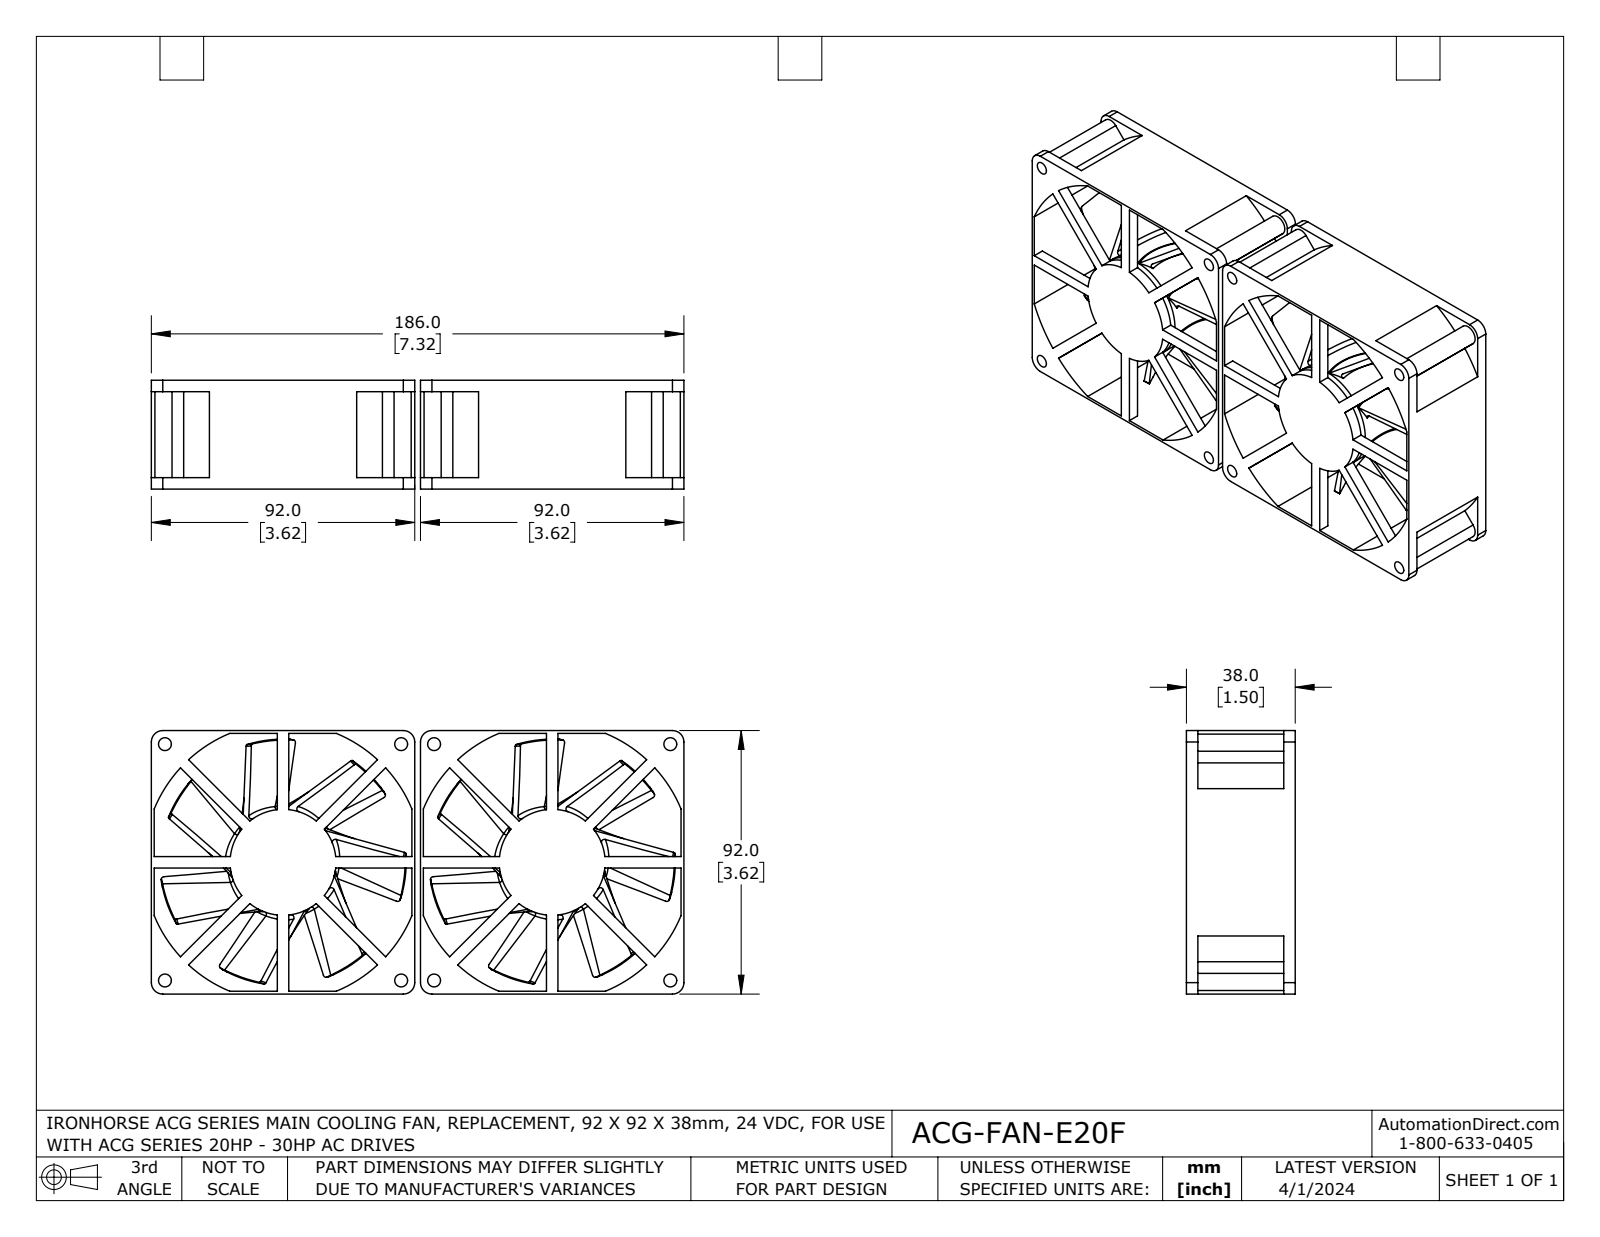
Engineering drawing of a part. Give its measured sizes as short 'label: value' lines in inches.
name: ACG-FAN-E20F
written by: SolidWorks 2021 (AUTOMOTIVE_DESIGN)
unit: in
bodies: 4 solids, 394 faces (92 planar, 106 cylindrical, 196 other)
size: 7.323 × 3.622 × 1.496
volume: 10.81 in³; area: 171.3 in²
holes: 8× ⌀0.177, 2× ⌀1.339
bosses: 2× ⌀1.457
rounds: 8× R0.138, 8× R0.157, 2× R1.917, 2× R2.075
face distances: 0.039, 3.583, 3.622, 3.701, 0.157, 3.543, 1.496, 0.118, 0.079, 1.339
hole spacings: 2.297, 3.248, 3.701, 2.636, 4.593, 4.924, 5.567, 0.453
